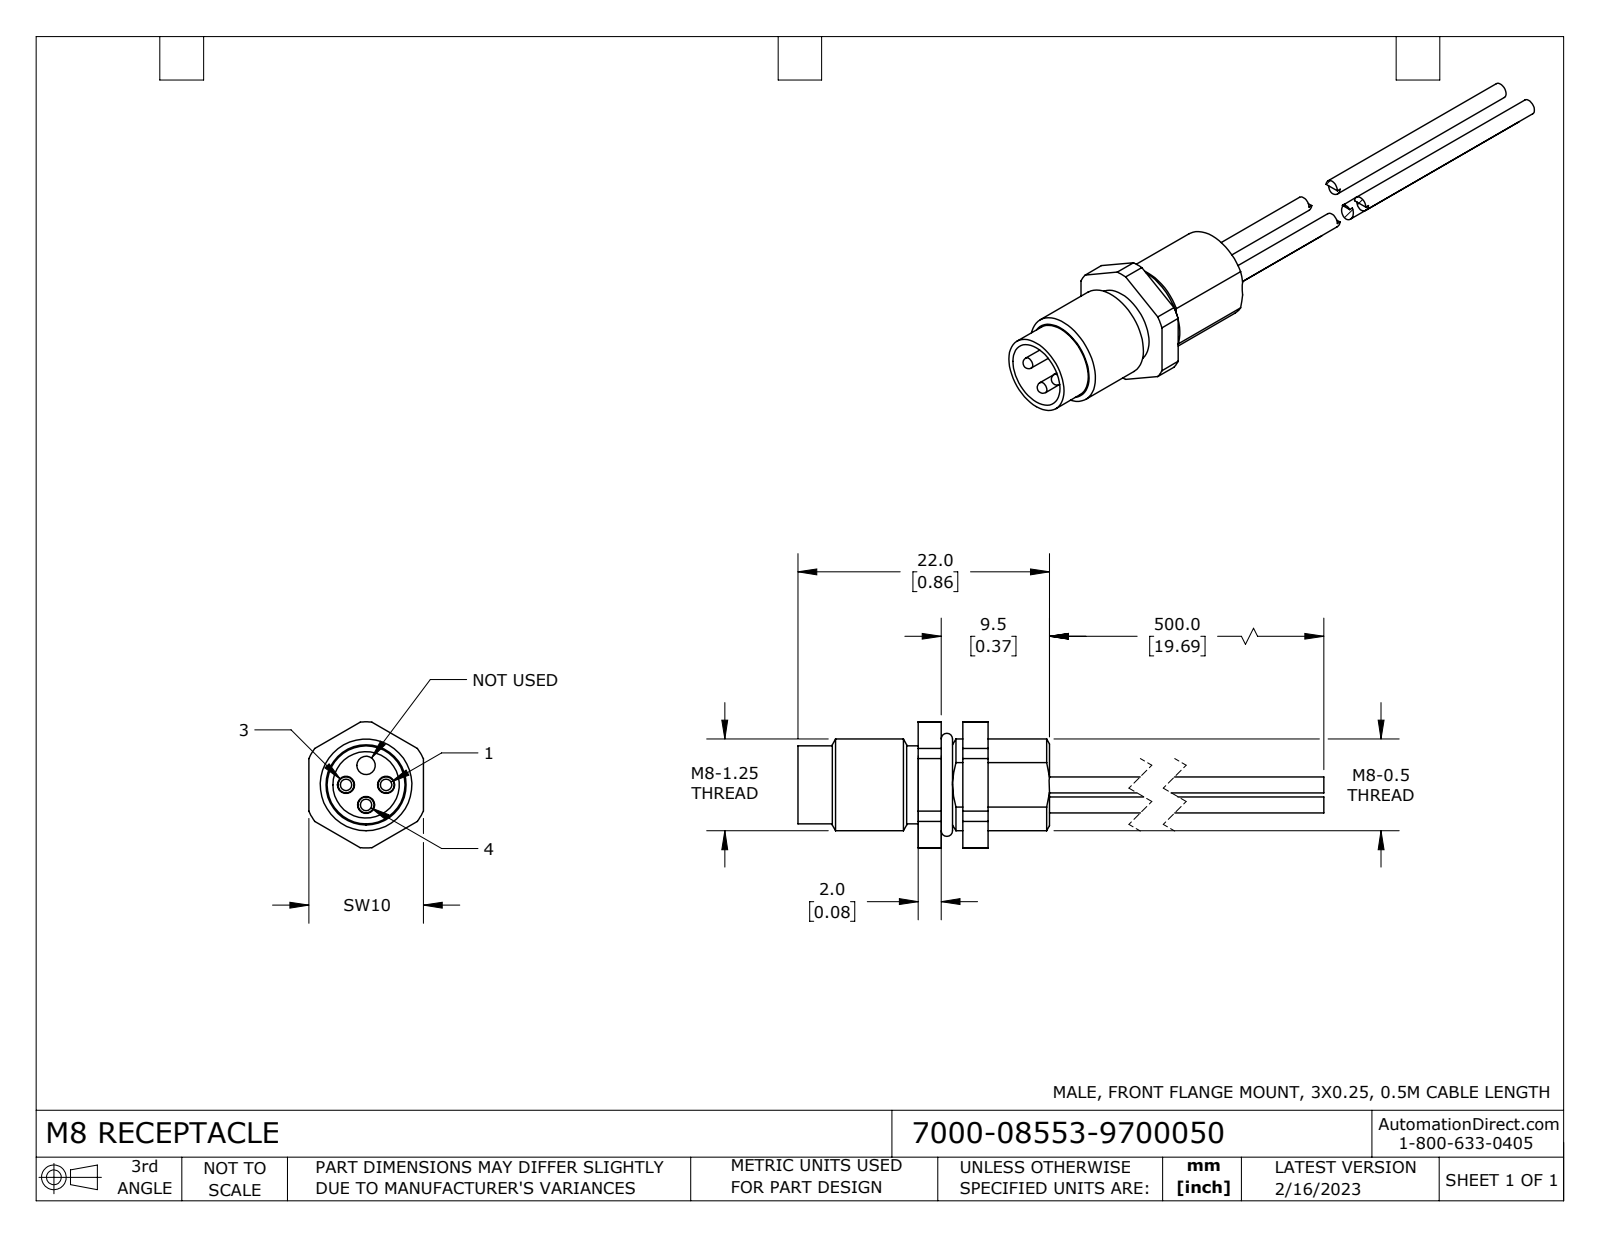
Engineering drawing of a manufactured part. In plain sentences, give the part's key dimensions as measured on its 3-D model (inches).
The part is named "7000-08553-9700050". Its 3-D file was written by "SolidWorks 2021 (CONFIG_CONTROL_DESIGN)". It is 9 solids with 107 faces: 34 planar, 51 cylindrical and 22 other. Overall it measures 4.724 by 0.433 by 0.394 inches. Its volume is 0.083 cubic inches and its surface area 4.28 square inches. Round holes: 3 of diameter 0.059, 1 of diameter 0.063, 1 of diameter 0.228, 1 of diameter 0.244. Round bosses or shafts: 3 of diameter 0.055, 3 of diameter 0.039, 1 of diameter 0.315, 1 of diameter 0.268. Partial cylindrical surfaces (rounded edges, fillets, slot ends): 1 of radius 0.217. The main face-to-face distances are 0.394, 0.079, 0.295, 0.335, 0.059, 0.276, 0.075, 0.154, 0.087, 0.161. The hole center spacings are 0.069, 0.096, 0.097, 0.067, 0.136, 0.138.
